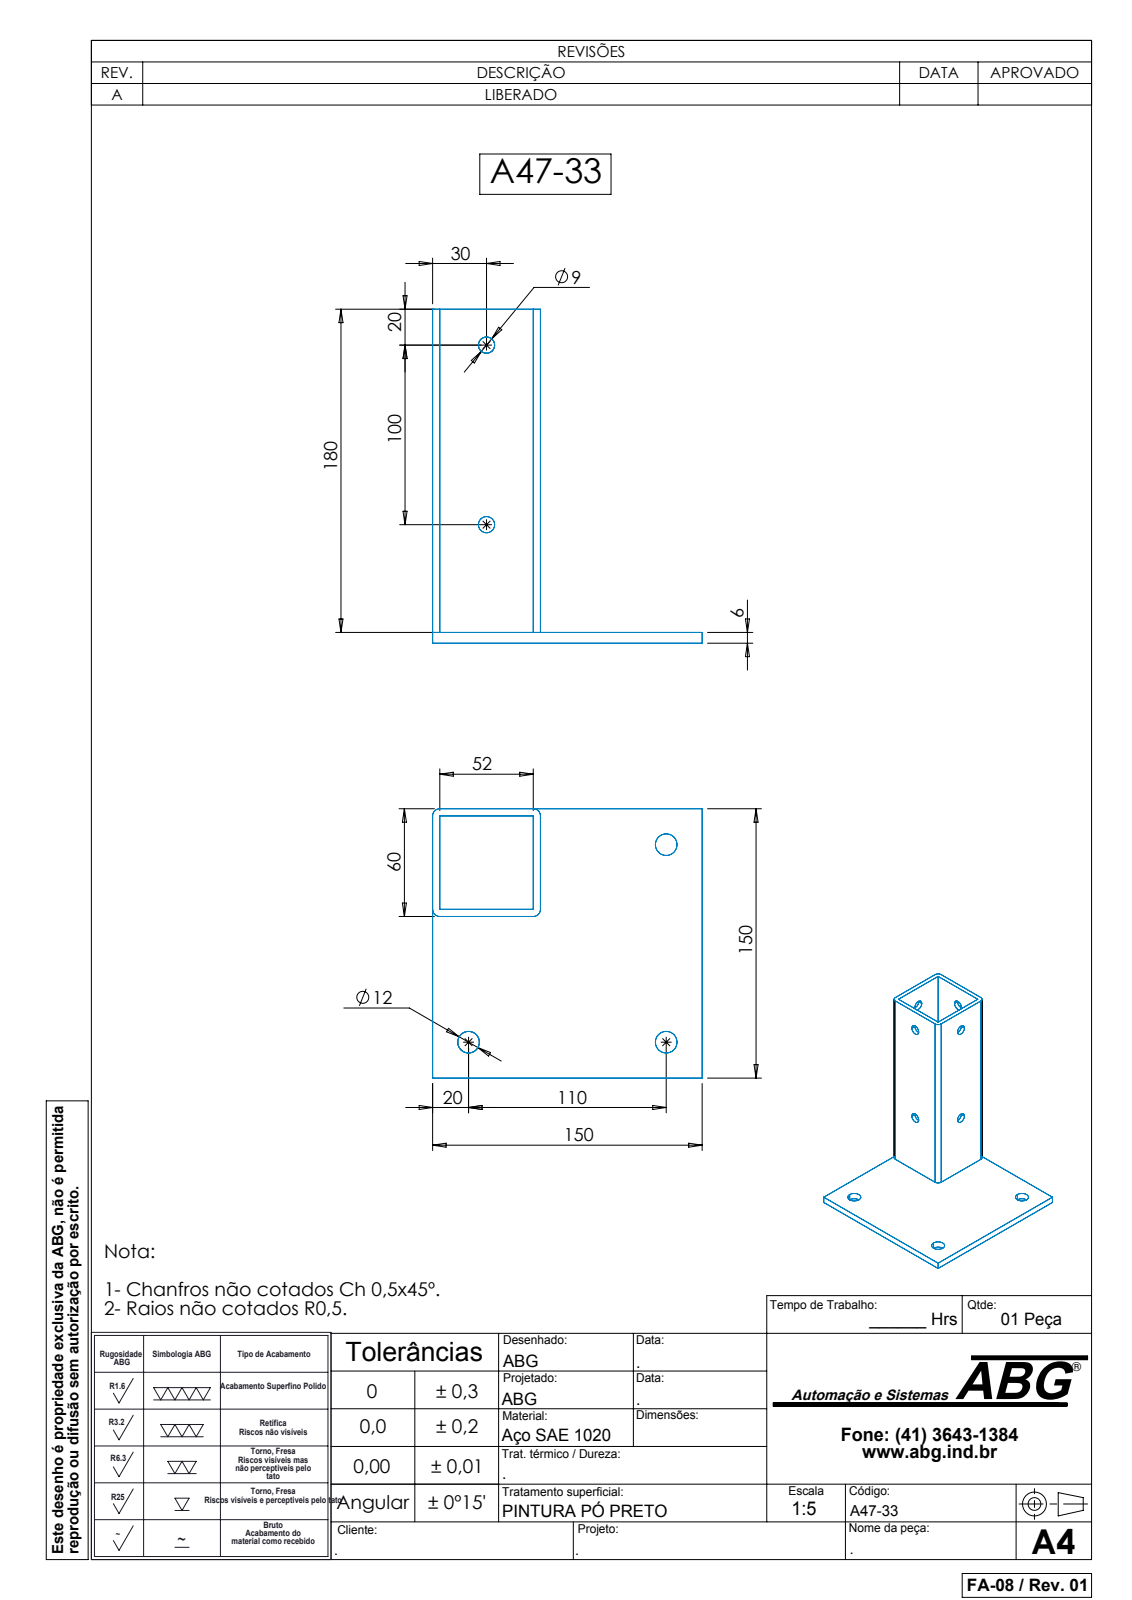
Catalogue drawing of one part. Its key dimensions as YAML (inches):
part_name: "A47-33"
step_written_by: "SolidWorks 2007 (CONFIG_CONTROL_DESIGN)"
units: inches
bodies: {solids: 1, faces: 40, planar: 14, cylindrical: 26, other: 0}
overall_size: [7.323, 5.906, 5.906]
volume: 17.68
surface_area: 198.2
round_holes:
  - {diameter: 0.354, count: 4}
  - {diameter: 0.472, count: 3}
partial_cylinders:
  - {radius: 0.157, count: 4}
face_to_face_distances: [0.157, 2.205, 0.236, 2.362, 2.047, 3.543, 3.701, 5.748, 5.906, 7.323]
hole_center_spacings: [3.937, 4.331, 6.124]
